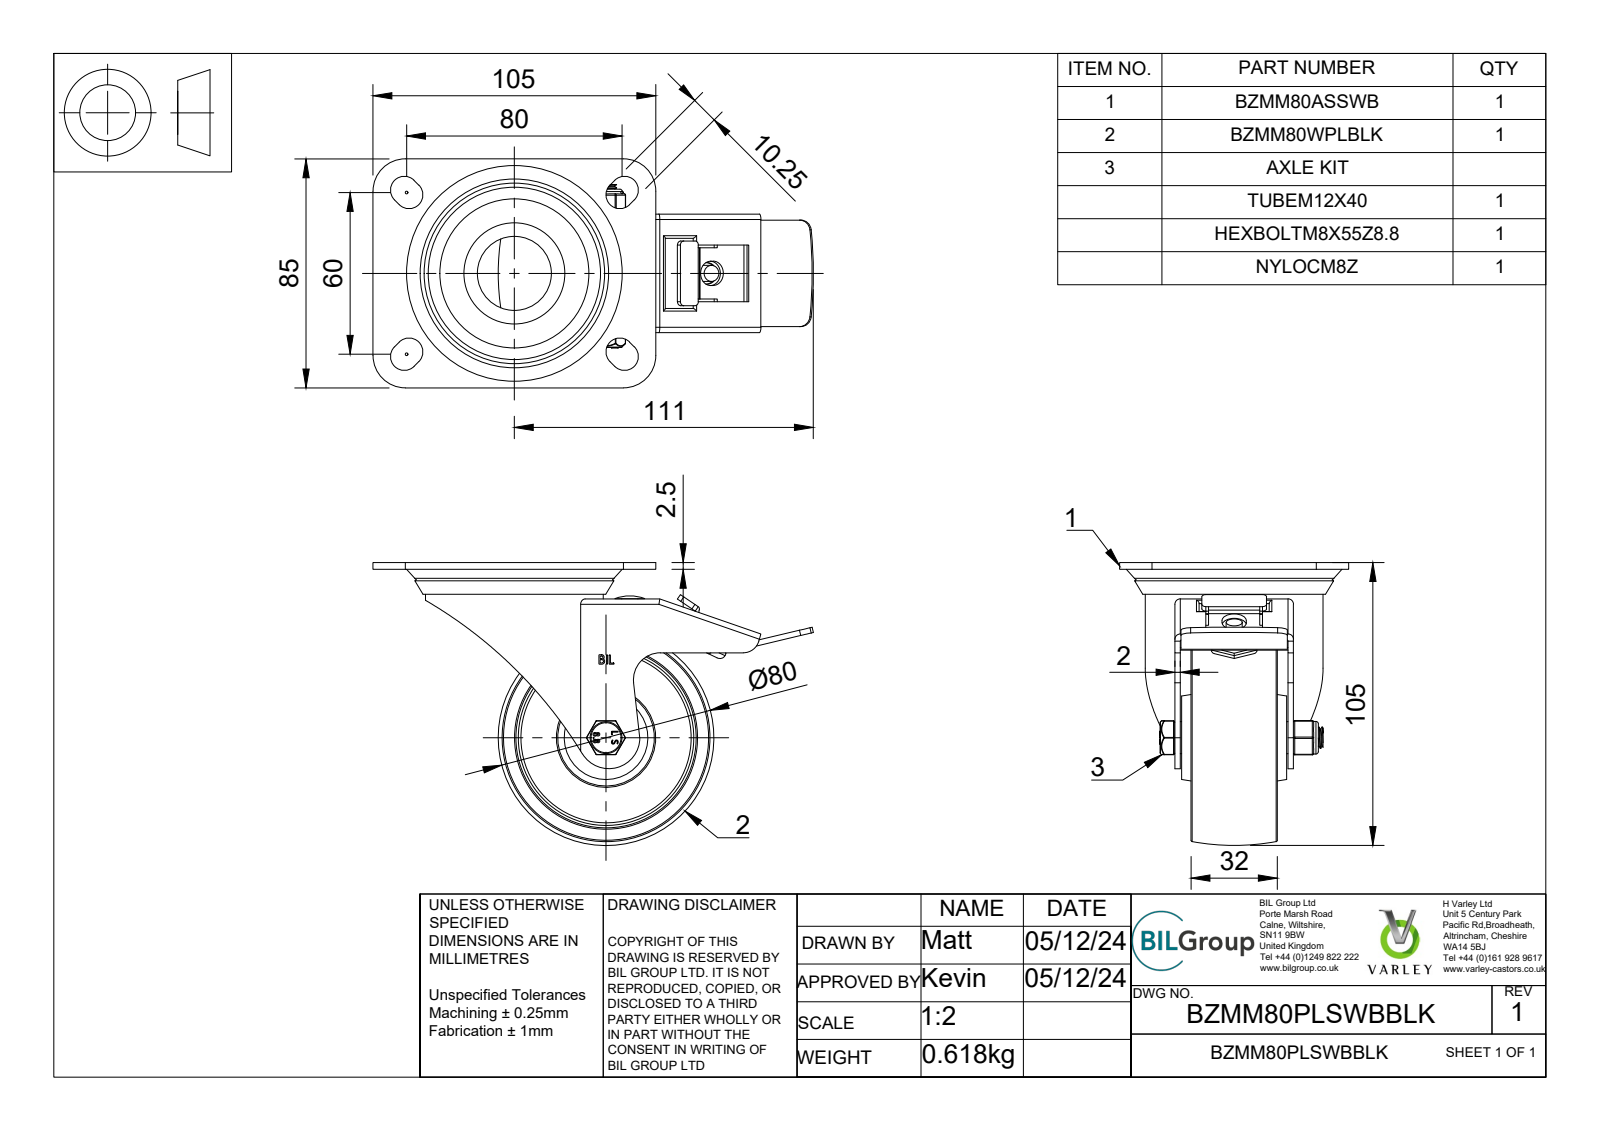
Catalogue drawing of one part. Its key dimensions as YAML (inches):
part_name: "BZMM80PLSWBBLK v3; BZMM80ASSWB v1; ZINC PLATED, PRESSED STEEL TOP PLATE; ZINC PLATED, PRESSED STEEL TOP PLATE Geometry (+7 more)"
step_written_by: "Autodesk Translation Framework v13.20.0.188 (AP242_MANAGED_MODEL_BASED_3D_ENGINEERING_MIM_LF)"
units: inches
bodies: {solids: 37, faces: 593, planar: 291, cylindrical: 178, other: 124}
overall_size: [6.437, 4.134, 3.346]
volume: 10.11
surface_area: 147.5
round_holes:
  - {diameter: 0.026, count: 2}
  - {diameter: 0.315, count: 2}
  - {diameter: 0.236, count: 1}
  - {diameter: 0.323, count: 1}
  - {diameter: 0.331, count: 1}
  - {diameter: 0.339, count: 1}
  - {diameter: 0.48, count: 1}
  - {diameter: 1.083, count: 1}
  - {diameter: 2.205, count: 1}
  - {diameter: 2.441, count: 1}
round_bosses_or_shafts:
  - {diameter: 2.598, count: 1}
  - {diameter: 1.24, count: 1}
  - {diameter: 0.476, count: 1}
  - {diameter: 0.469, count: 1}
  - {diameter: 0.453, count: 1}
  - {diameter: 0.31, count: 1}
  - {diameter: 0.254, count: 1}
  - {diameter: 0.236, count: 1}
partial_cylinders:
  - {radius: 0.02, count: 24}
  - {radius: 0.039, count: 14}
  - {radius: 0.01, count: 12}
  - {radius: 0.079, count: 11}
  - {radius: 0.202, count: 8}
  - {radius: 0.013, count: 4}
  - {radius: 0.025, count: 4}
  - {radius: 0.059, count: 4}
face_to_face_distances: [0.079, 0.098, 0.65, 0.02, 0.728, 1.004, 1.654, 0.925, 0.512, 0.236]
hole_center_spacings: [0.127, 0.098, 1.687]
